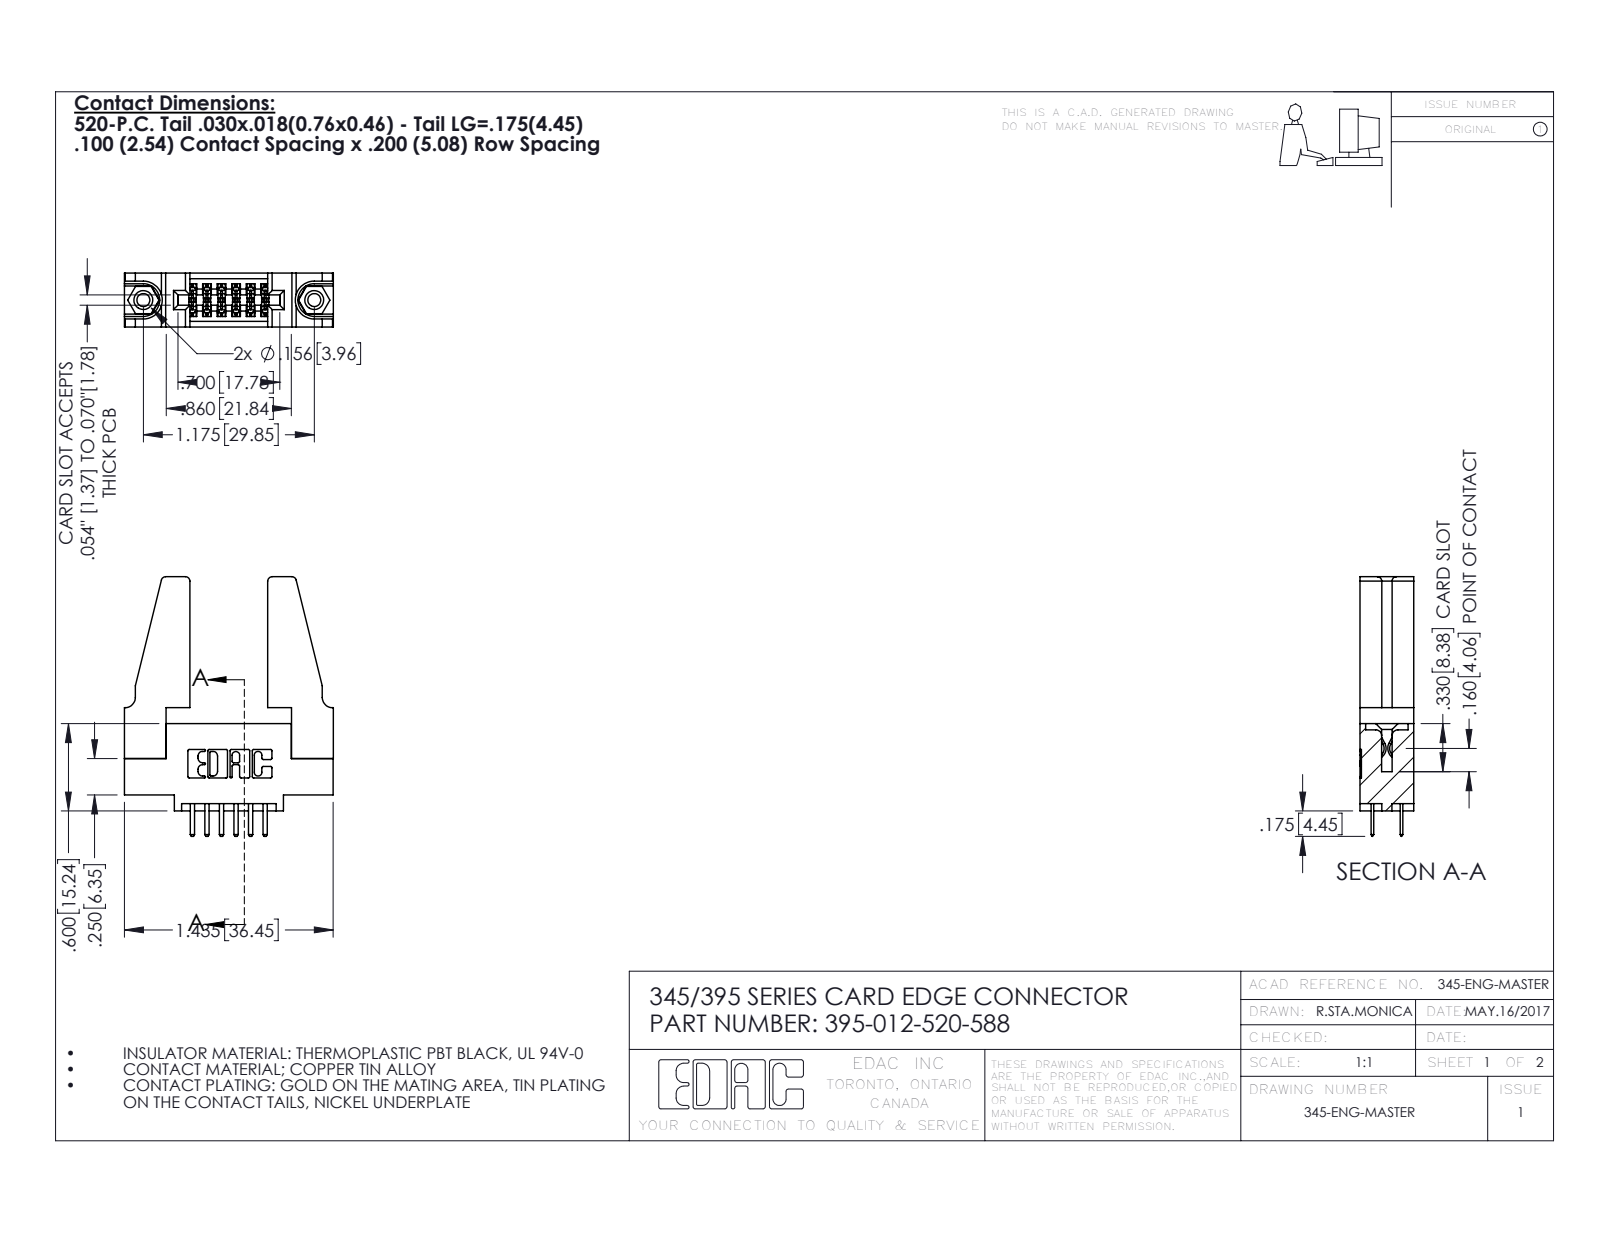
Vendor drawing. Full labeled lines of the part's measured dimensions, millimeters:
Part name (STEP PRODUCT): 345-292-001_345-293-120; 395-012-520-588; 345 Part_0.110 Offset - 0.156 Dia-TH; 345-250-001_345-250-001-102 (+1 more)
STEP written by: SolidWorks 2016 (CONFIG_CONTROL_DESIGN)
Units: millimetres
Bodies: 17 solids, 902 faces (576 planar, 310 cylindrical, 16 other)
Overall size (bounding box): 45.3 × 36.5 × 9.4
Volume: 6 390 mm³ · Surface area: 7 135 mm²
Round holes (diameter × count): ⌀2.3 ×2, ⌀3.2 ×2, ⌀4 ×2, ⌀1.6 ×1
Round bosses / shafts (diameter × count): ⌀3.9 ×2
Partial cylindrical surfaces — rounded edges, fillets, slot ends (radius × count): R0.3 ×22, R0.2 ×18, R0.3 ×16, R0.8 ×8, R0.2 ×6, R0.8 ×6, R0.7 ×3, R0.4 ×2
Main face-to-face distances: 9.4, 1.8, 7.6, 5.1, 5.7, 3.8, 5.6, 2, 3.8, 2.5
Hole centre spacings: 6.9, 24, 29.8
